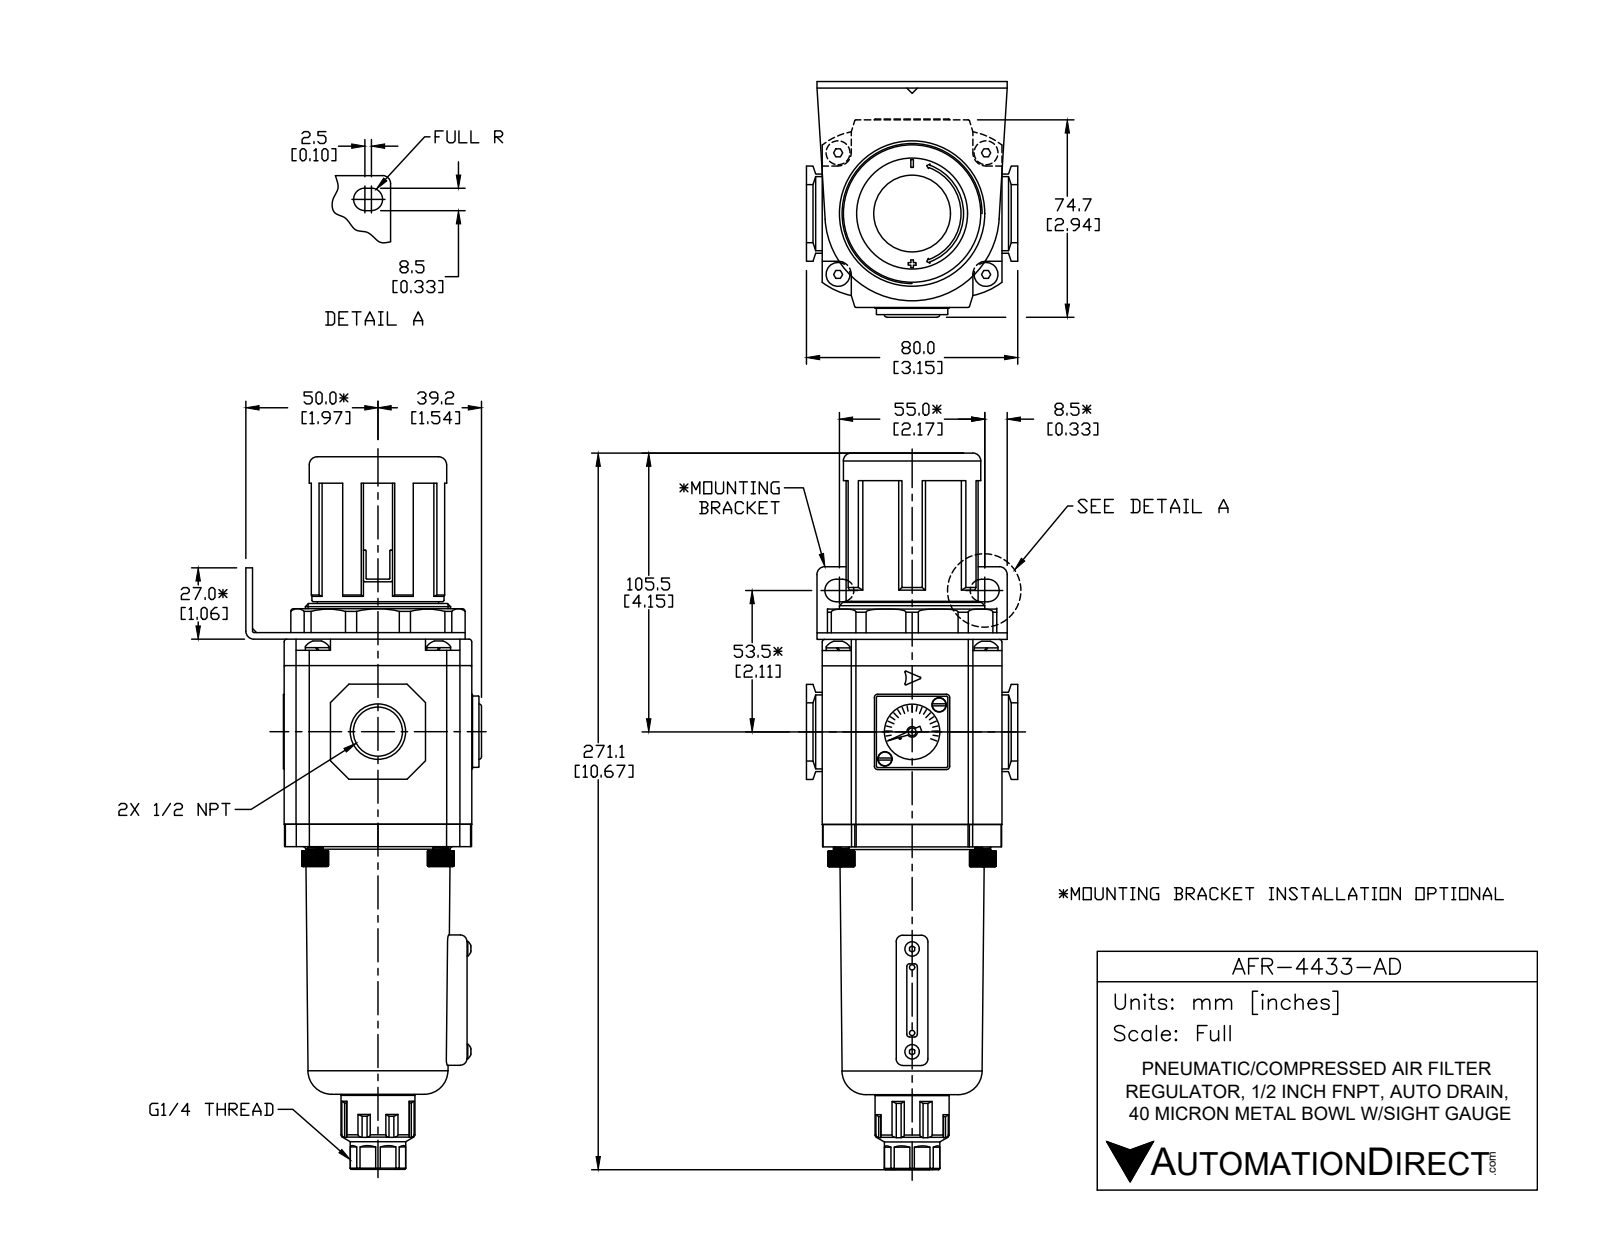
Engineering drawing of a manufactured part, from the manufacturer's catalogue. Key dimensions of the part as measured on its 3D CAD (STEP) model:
Part name (STEP PRODUCT): AFR-4433-AD
STEP written by: SolidWorks 2015 (CONFIG_CONTROL_DESIGN)
Units: millimetres
Bodies: 16 solids, 683 faces (417 planar, 177 cylindrical, 89 other)
Overall size (bounding box): 269.6 × 88.2 × 80
Volume: 750 992 mm³ · Surface area: 105 334 mm²
Round holes (diameter × count): ⌀3 ×6, ⌀2 ×1, ⌀12 ×1, ⌀17.86 ×1, ⌀21 ×1, ⌀30 ×1
Round bosses / shafts (diameter × count): ⌀10 ×4, ⌀9 ×4, ⌀5.5 ×2, ⌀2.7 ×2, ⌀55 ×1, ⌀52 ×1, ⌀50 ×1, ⌀43.68 ×1
Partial cylindrical surfaces — rounded edges, fillets, slot ends (radius × count): R1 ×16, R1.2 ×10, R1.3 ×8, R2.5 ×8, R9.5 ×8, R19.9 ×8, R0.5 ×6, R0.3 ×4
Main face-to-face distances: 2.5, 70, 72.5, 71, 68, 74, 85.5, 8.5, 78.5, 81
Hole centre spacings: 33.3, 14.5, 42.6, 51.2, 66.6, 28.99
